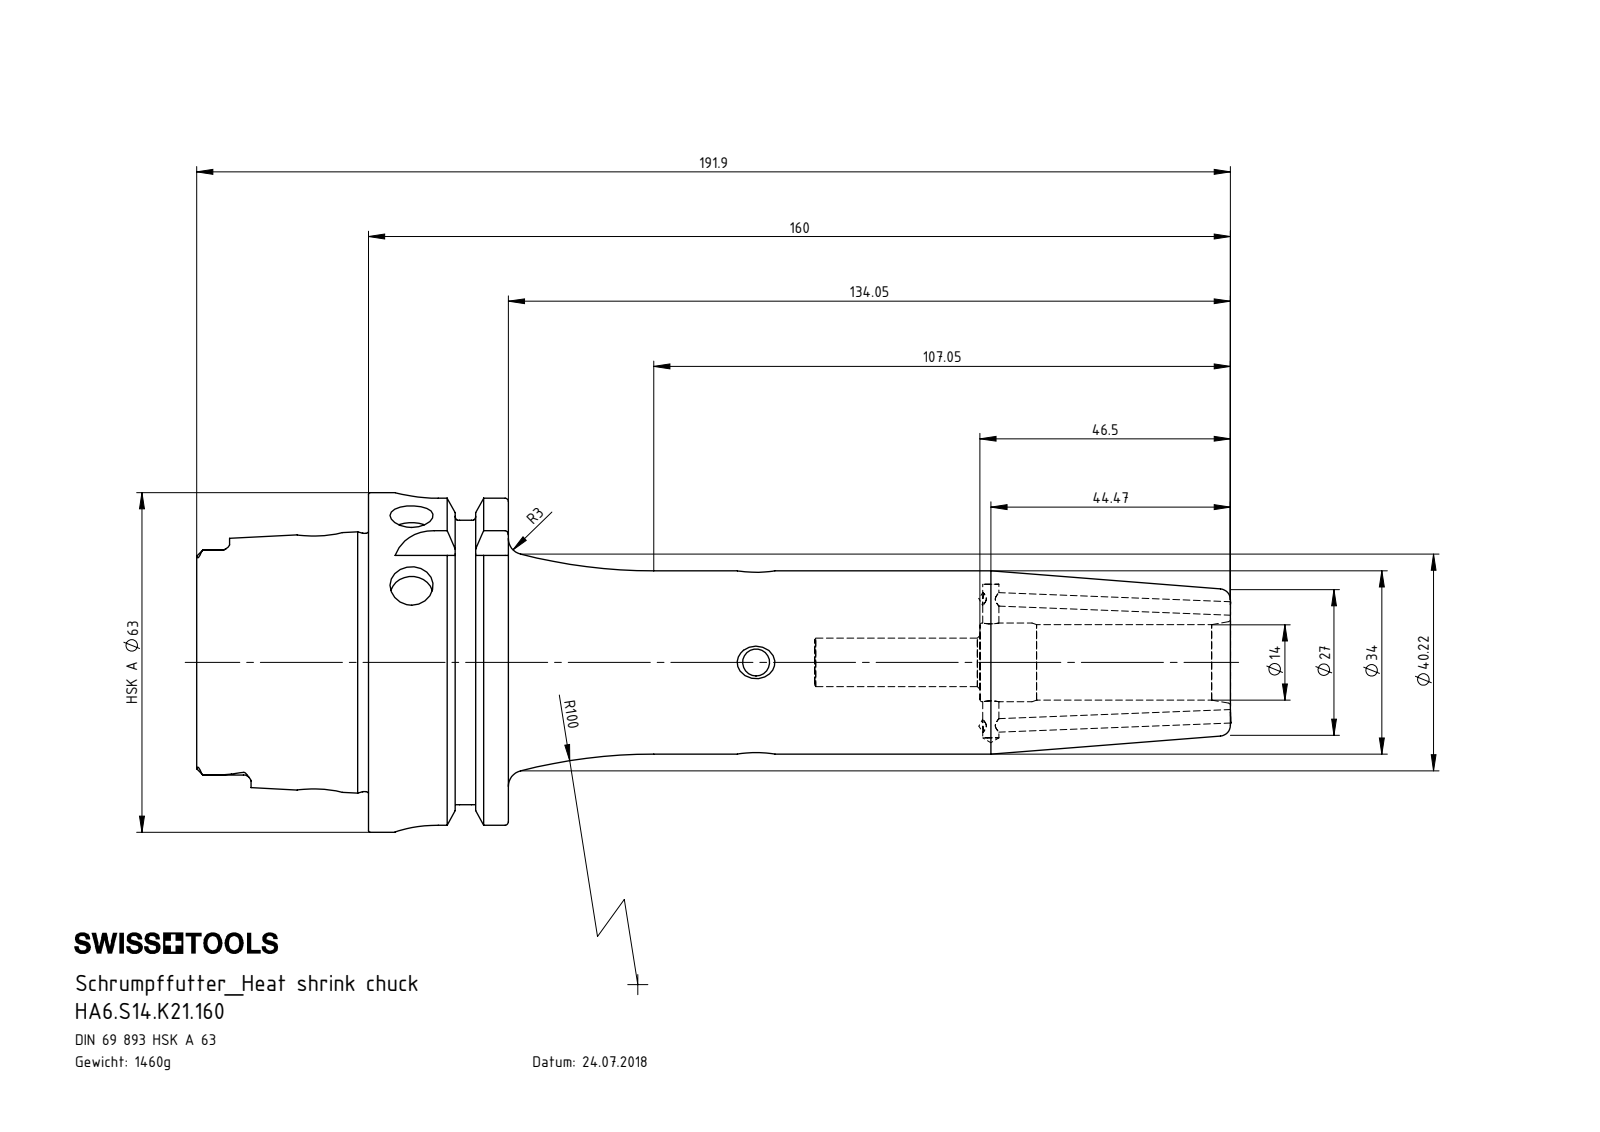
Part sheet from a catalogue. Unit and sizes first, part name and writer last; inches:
Units: inches
Overall size (bounding box): 7.558 × 2.48 × 2.48
Round holes (diameter × count): ⌀0.197 ×3, ⌀0.098 ×2, ⌀0.315 ×2, ⌀0.118 ×1, ⌀0.295 ×1, ⌀0.331 ×1, ⌀0.354 ×1, ⌀0.394 ×1, ⌀0.551 ×1, ⌀0.575 ×1, ⌀0.669 ×1, ⌀0.748 ×1
Round bosses / shafts (diameter × count): ⌀0.118 ×2, ⌀2.48 ×1, ⌀2.163 ×1, ⌀1.887 ×1, ⌀0.394 ×1
Partial cylindrical surfaces — rounded edges, fillets, slot ends (radius × count): R0.055 ×6, R0.113 ×4, R0.315 ×4
Main face-to-face distances: 1.022, 0.63, 0.392, 1.256, 1.648, 2.278, 2.079, 0.858, 0.467, 2.114
Hole centre spacings: 1.715, 2.557, 3.187, 4.902
Volume: 11.35 in³ · Surface area: 66.02 in²
Bodies: 4 solids, 319 faces (101 planar, 87 cylindrical, 131 other)
Part name (STEP PRODUCT): HA6-S14.K21.160; ERU-AN4.K01.020_A; ERU-CJ2.001.006; HA6-S14.K21.160_D_Fertigbearbeitung
STEP written by: SolidWorks 2012 (CONFIG_CONTROL_DESIGN)
